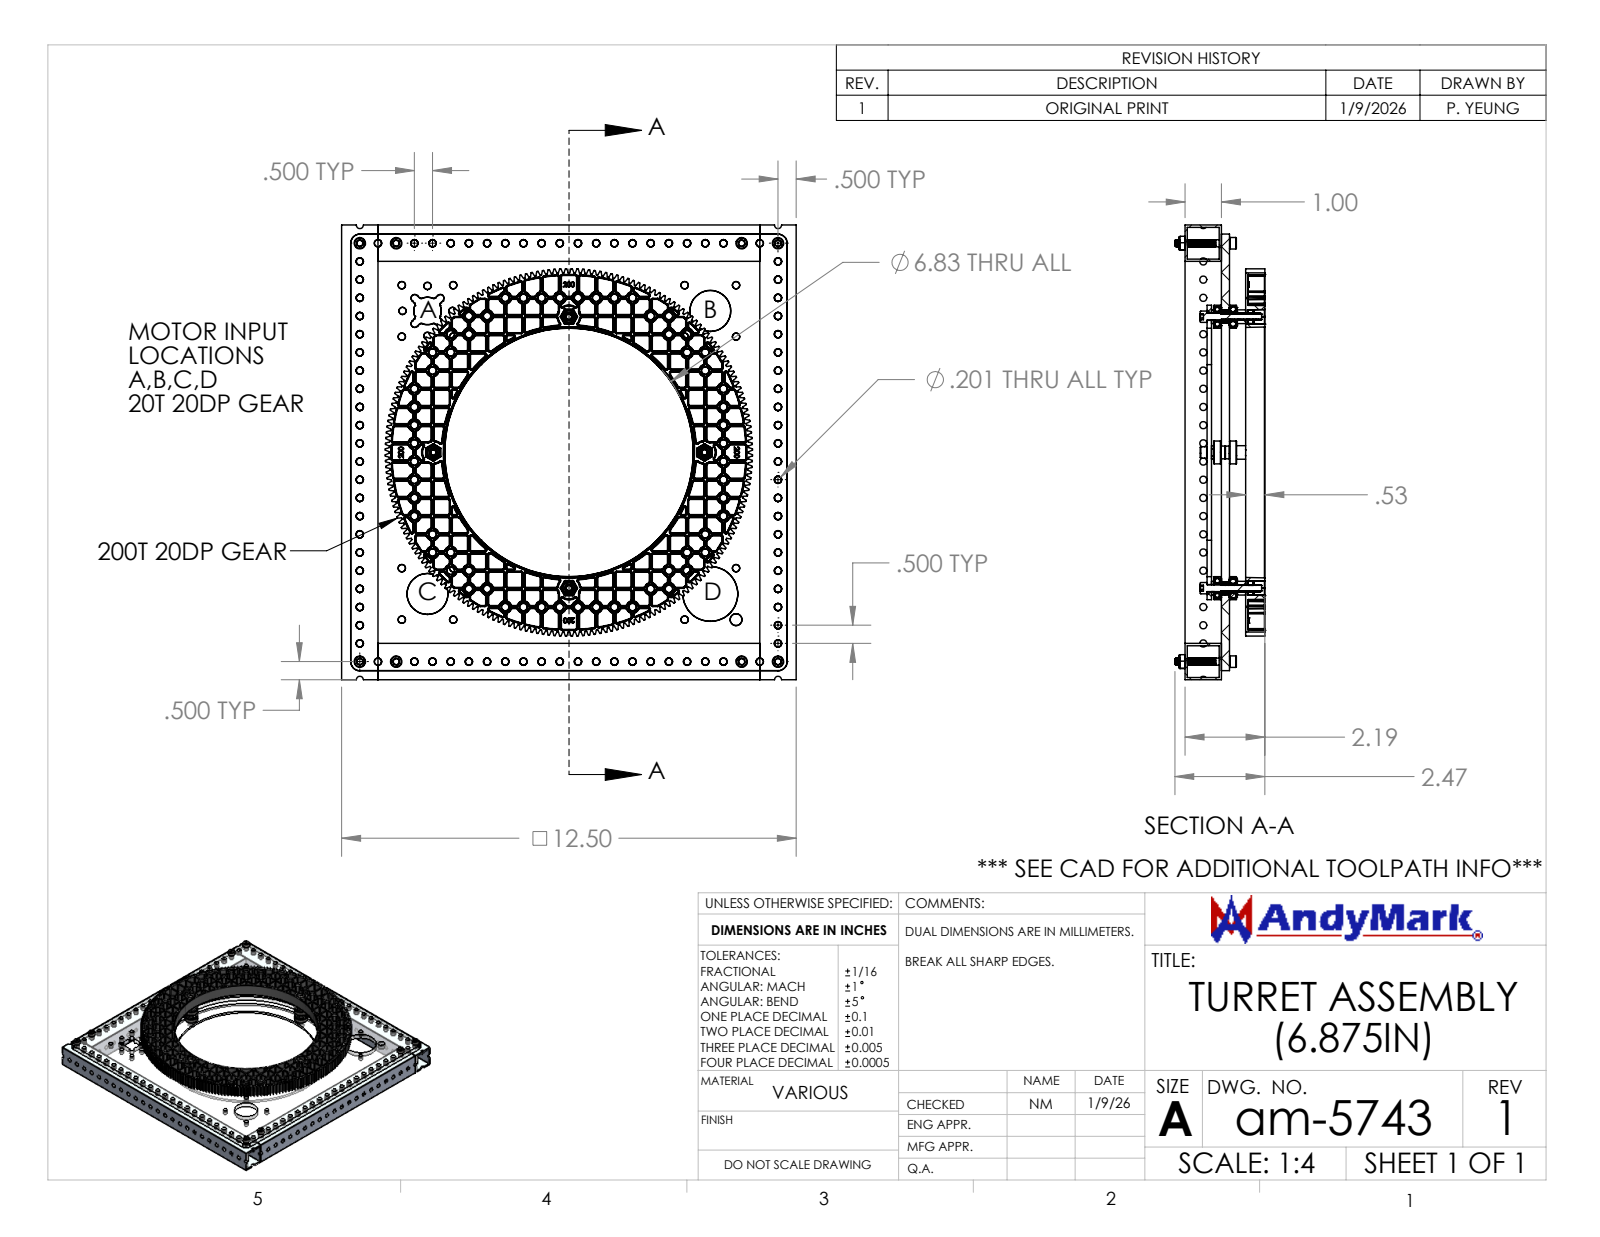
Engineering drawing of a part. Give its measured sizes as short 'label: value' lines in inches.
name: am-5693 5mm ID x 9mm OD x 3mm Thick Flanged Bearing (95-2Z)_am-5693 5mm ID x 9mm OD x 3mm Thick Flanged Bearing (95-2Z); 1x1 Turret Tube (10.5IN); am-5745 6.875IN Turret Support Ring; am-5038 200T 20DP Turntable Gear (+8 more)
written by: SolidWorks 2024 (AUTOMOTIVE_DESIGN)
unit: in
bodies: 283 solids, 12732 faces (1714 planar, 4937 cylindrical, 6081 other)
size: 12.5 × 12.5 × 2.474
volume: 40.98 in³; area: 901.8 in²
holes: 174× ⌀0.201, 132× ⌀0.196, 48× ⌀0.164, 12× ⌀0.161, 12× ⌀0.239, 4× ⌀0.192, 4× ⌀0.194, 4× ⌀0.197, 4× ⌀0.255, 4× ⌀0.282, 4× ⌀0.295, 4× ⌀0.296
bosses: 12× ⌀0.312, 12× ⌀0.19, 4× ⌀0.63, 4× ⌀0.498, 4× ⌀0.375, 4× ⌀0.354, 1× ⌀8.091
rounds: 400× R2, 224× R0.01, 12× R0.082, 12× R0.098, 4× R0.062, 4× R0.063, 4× R0.101, 4× R0.25
face distances: 0.063, 0.937, 1, 0.22, 11.5, 0.875, 1.667, 0.73, 0.5, 1.22
hole spacings: 1, 0.5, 2, 1.5, 2.5, 3, 3.5, 4
